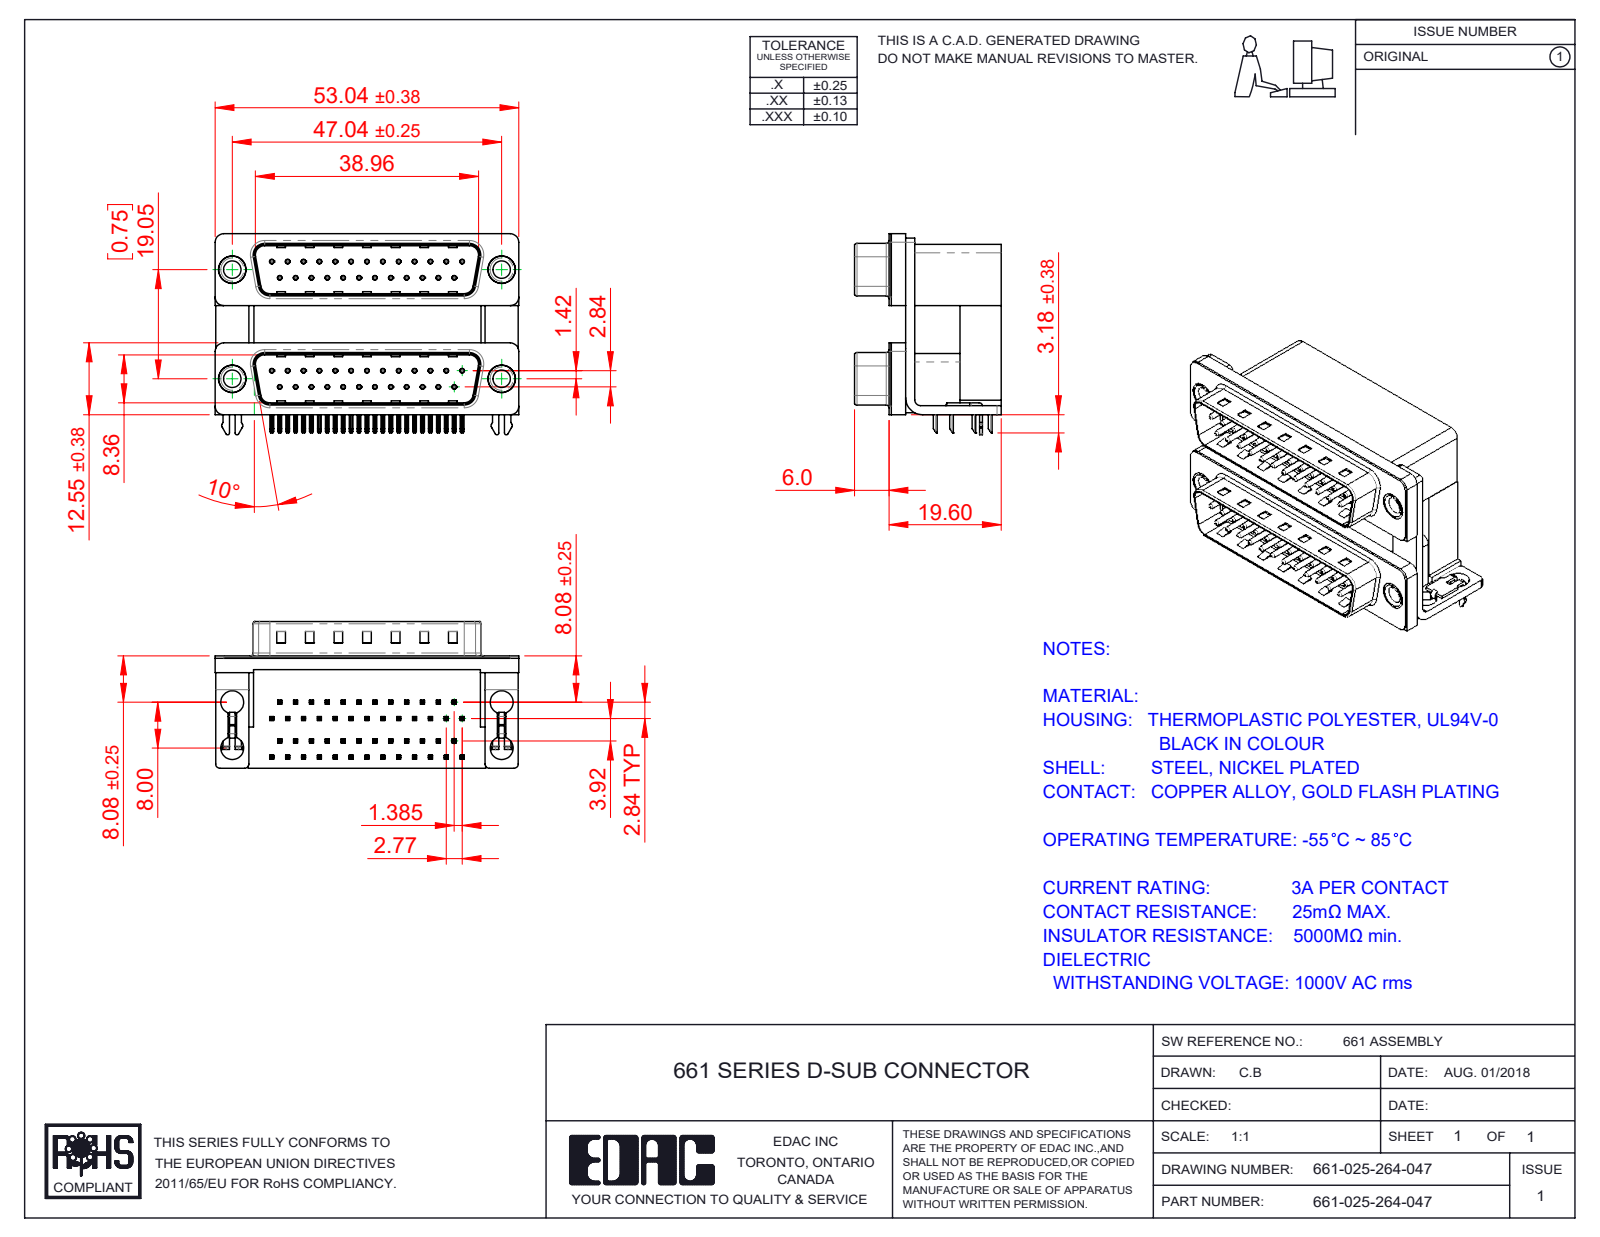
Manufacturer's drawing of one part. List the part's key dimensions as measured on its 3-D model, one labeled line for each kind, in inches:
Part name (STEP PRODUCT): 661 Contact Bottom Lower; 661 Contact Bottom Upper_M; 661 Housing Lower_25 Contacts; 661 Housing Spacer_25 Contacts M (+8 more)
STEP written by: SolidWorks 2020 (CONFIG_CONTROL_DESIGN)
Units: inches
Bodies: 65 solids, 4722 faces (3034 planar, 1310 cylindrical, 378 other)
Overall size (bounding box): 2.088 × 1.374 × 1.008
Volume: 1.298 in³ · Surface area: 34.79 in²
Round holes (diameter × count): ⌀0.014 ×50, ⌀0.031 ×50, ⌀0.079 ×4, ⌀0.098 ×4, ⌀0.12 ×4, ⌀0.126 ×4, ⌀0.138 ×4, ⌀0.157 ×4, ⌀0.189 ×4, ⌀0.197 ×4
Round bosses / shafts (diameter × count): ⌀0.03 ×50, ⌀0.193 ×4, ⌀0.187 ×4, ⌀0.157 ×4, ⌀0.152 ×4, ⌀0.134 ×4, ⌀0.13 ×4, ⌀0.114 ×4
Partial cylindrical surfaces — rounded edges, fillets, slot ends (radius × count): R0.01 ×200, R0.005 ×100, R0.02 ×16, R0.059 ×14, R0.03 ×8, R0.035 ×8, R0.063 ×8, R0.079 ×8
Main face-to-face distances: 0.016, 0.756, 0.75, 0.283, 0.472, 0.421, 0.657, 0.374, 0.098, 0.329
Hole centre spacings: 0.124, 0.109, 0.218, 0.327, 0.436, 0.545, 0.654, 0.198
